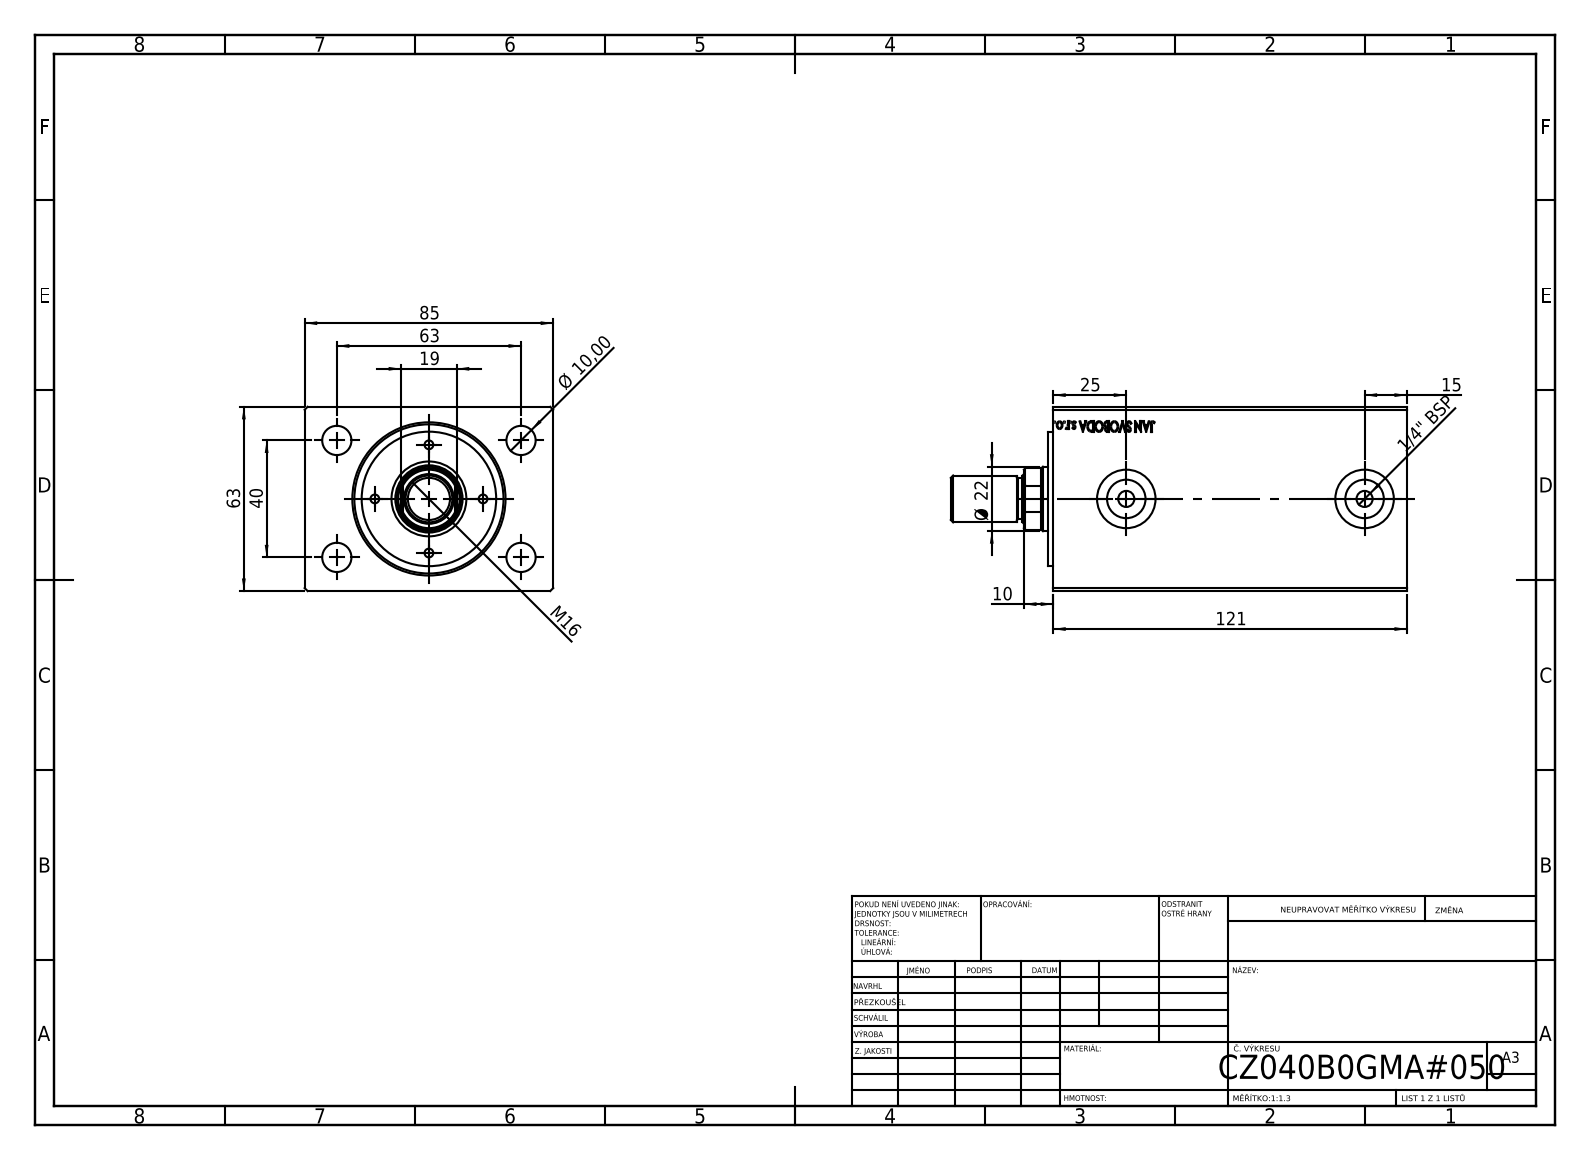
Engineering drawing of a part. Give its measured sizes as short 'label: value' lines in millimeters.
name: V500CZ_MALE_METRIC; V500CZ; V500CZ_B_VC
written by: SolidWorks 2019 (CONFIG_CONTROL_DESIGN)
unit: mm
bodies: 4 solids, 888 faces (404 planar, 62 cylindrical, 422 other)
size: 156 × 85 × 63
volume: 587 002 mm³; area: 88 989 mm²
holes: 4× ⌀3, 4× ⌀10, 2× ⌀5.5, 2× ⌀13.16, 2× ⌀20, 1× ⌀14.5, 1× ⌀22, 1× ⌀23, 1× ⌀36, 1× ⌀40, 1× ⌀51
bosses: 1× ⌀46, 1× ⌀16, 1× ⌀14
rounds: 1× R10.5
face distances: 63, 85, 121, 105.7, 15.3, 10, 8.2, 1.8, 97.5, 112.8
hole spacings: 18.5, 23.85, 26.16, 31.54, 37.31, 49.74, 53.85, 37
